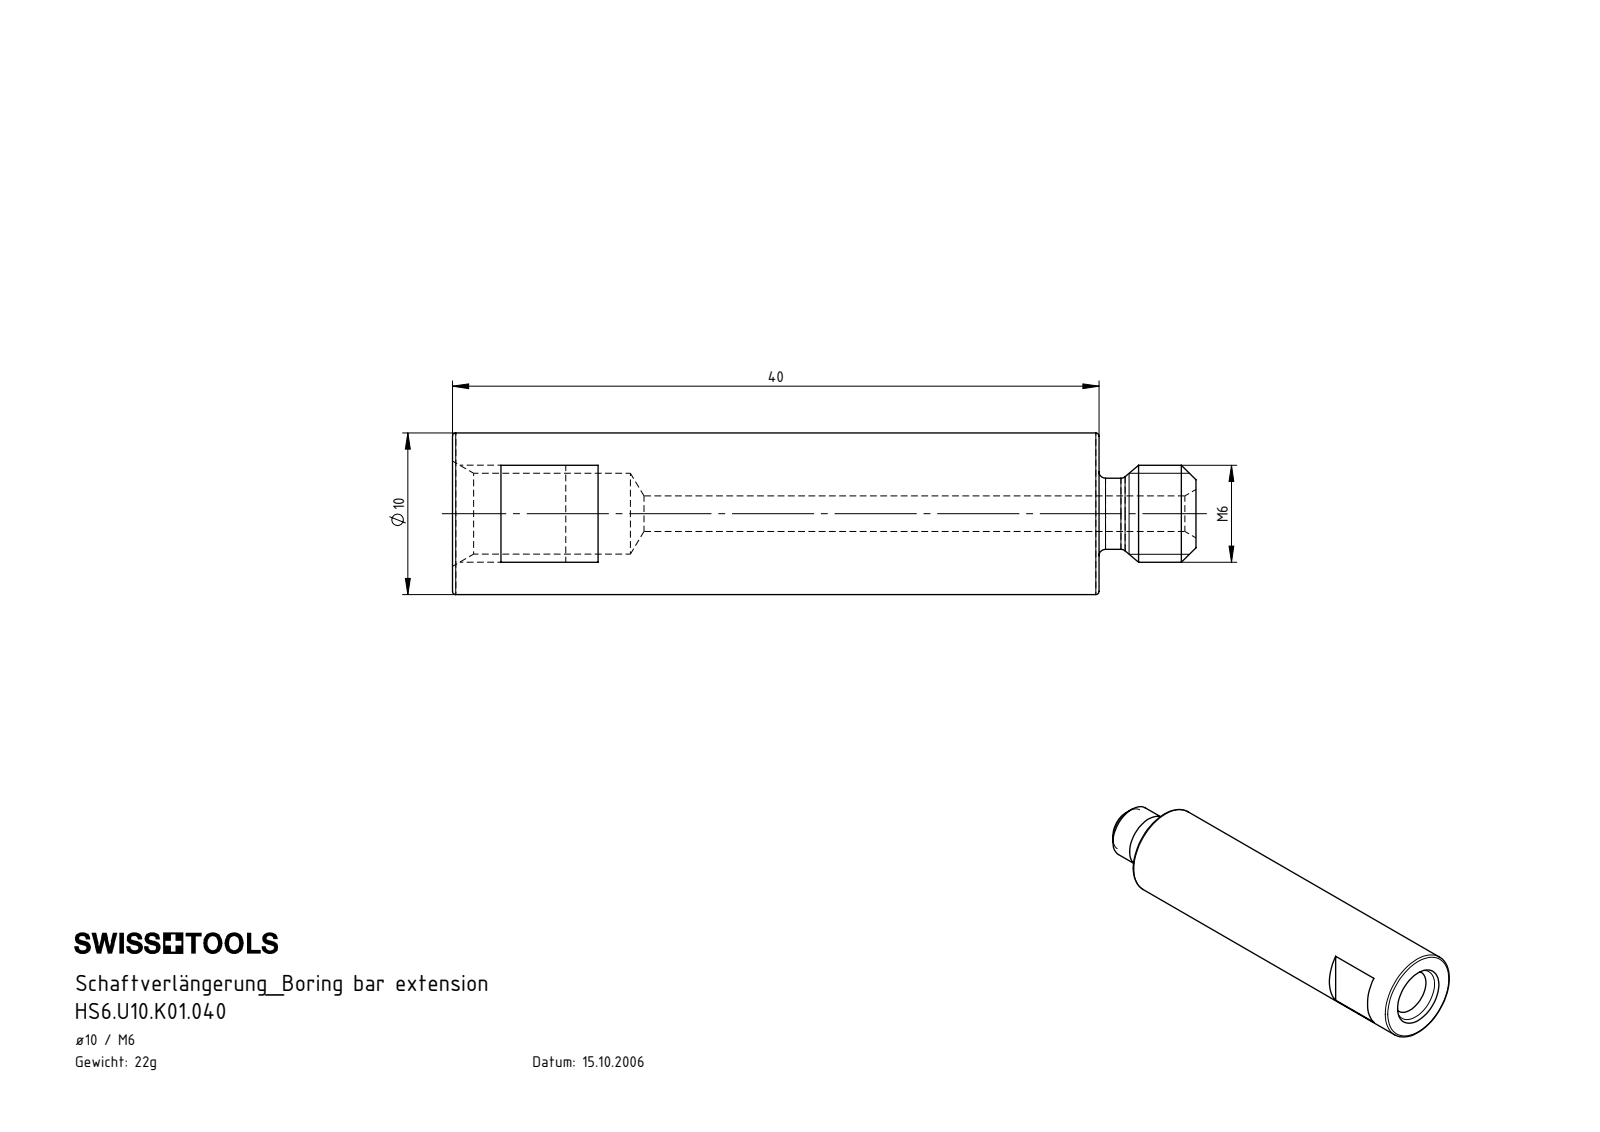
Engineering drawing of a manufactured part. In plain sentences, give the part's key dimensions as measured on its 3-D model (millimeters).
The part is named "HS6.U10.K01.040". Its 3-D file was written by "SolidWorks 2022 (CONFIG_CONTROL_DESIGN)". It is 1 solid with 37 faces: 9 planar, 10 cylindrical and 18 other. Overall it measures 46 by 10 by 10 millimeters. Its volume is 2 865 cubic millimeters and its surface area 1 922 square millimeters. Round holes: 1 of diameter 2.2, 1 of diameter 5. Round bosses or shafts: 1 of diameter 10, 1 of diameter 6, 1 of diameter 4.4. The main face-to-face distances are 40, 8, 37, 6, 3, 31, 9, 43, 46.
